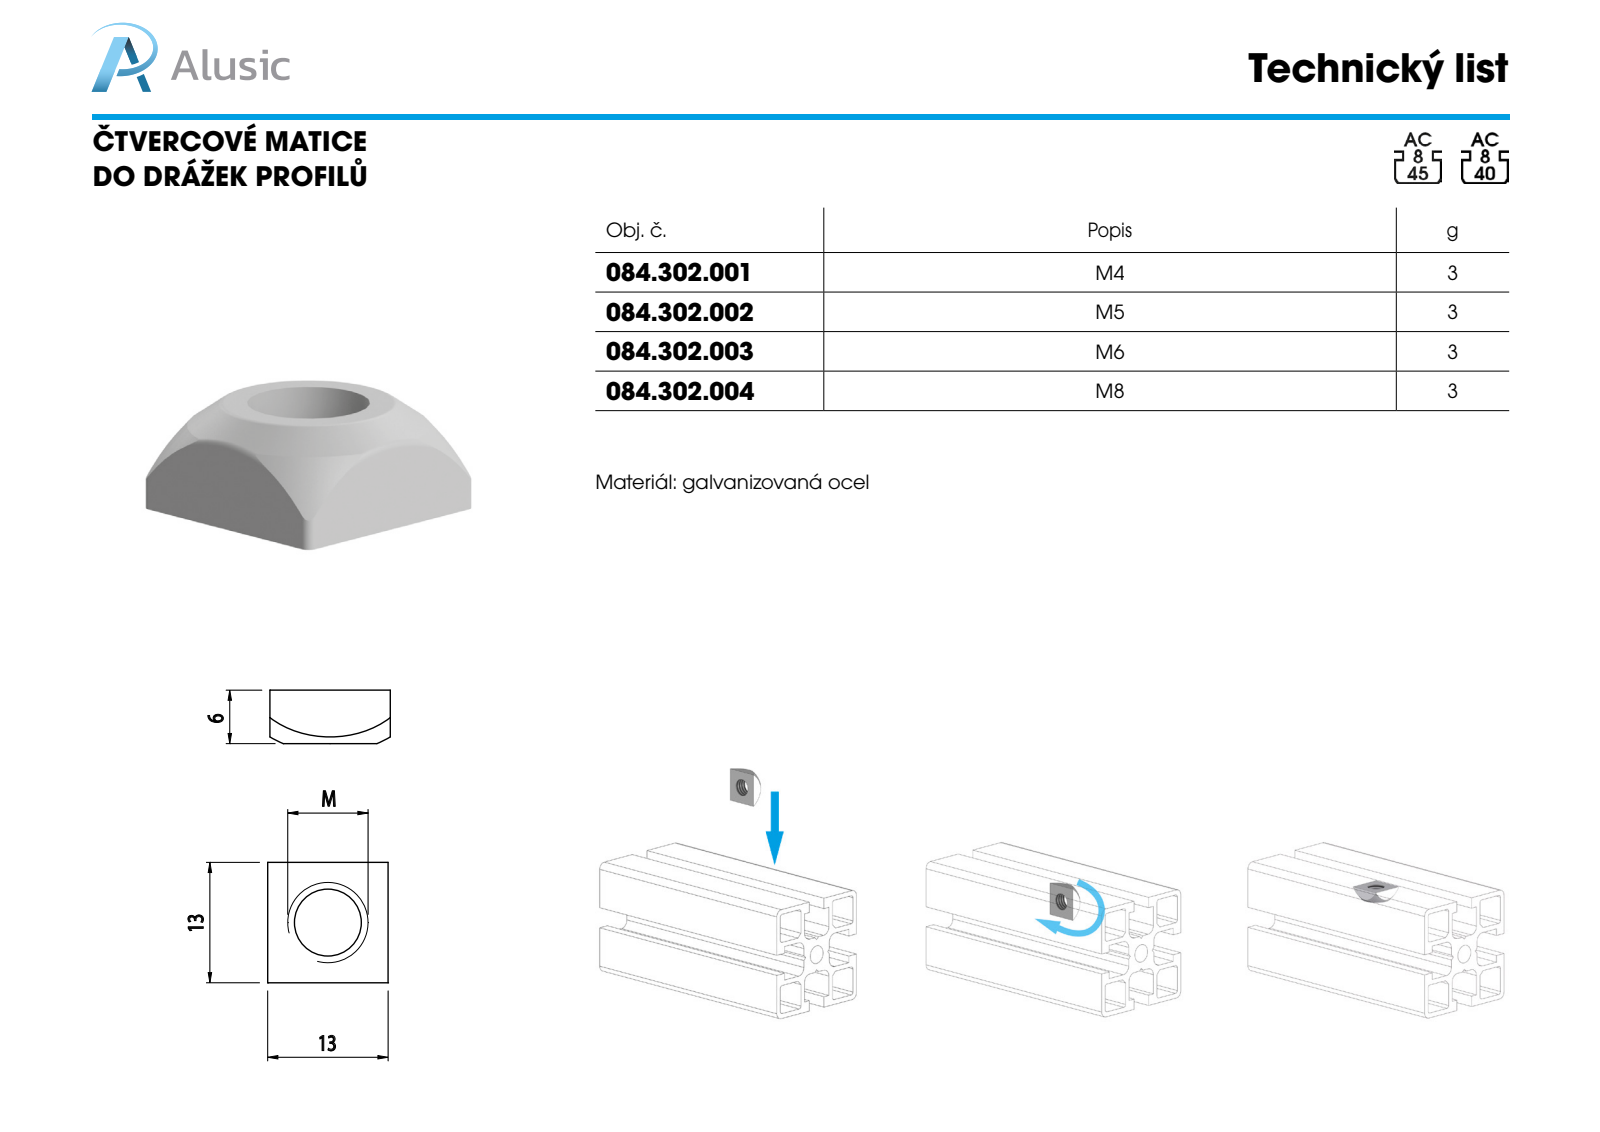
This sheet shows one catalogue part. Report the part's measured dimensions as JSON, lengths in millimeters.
{"part_name": "084.302.002", "step_written_by": "SolidWorks 2012 (CONFIG_CONTROL_DESIGN)", "units": "millimeters", "bodies": {"solids": 1, "faces": 12, "planar": 6, "cylindrical": 1, "other": 5}, "overall_size": [13, 13, 6], "volume_mm3": 821, "surface_area_mm2": 616, "round_holes": [[4.2, 1]], "face_to_face_distances": [13, 6]}
